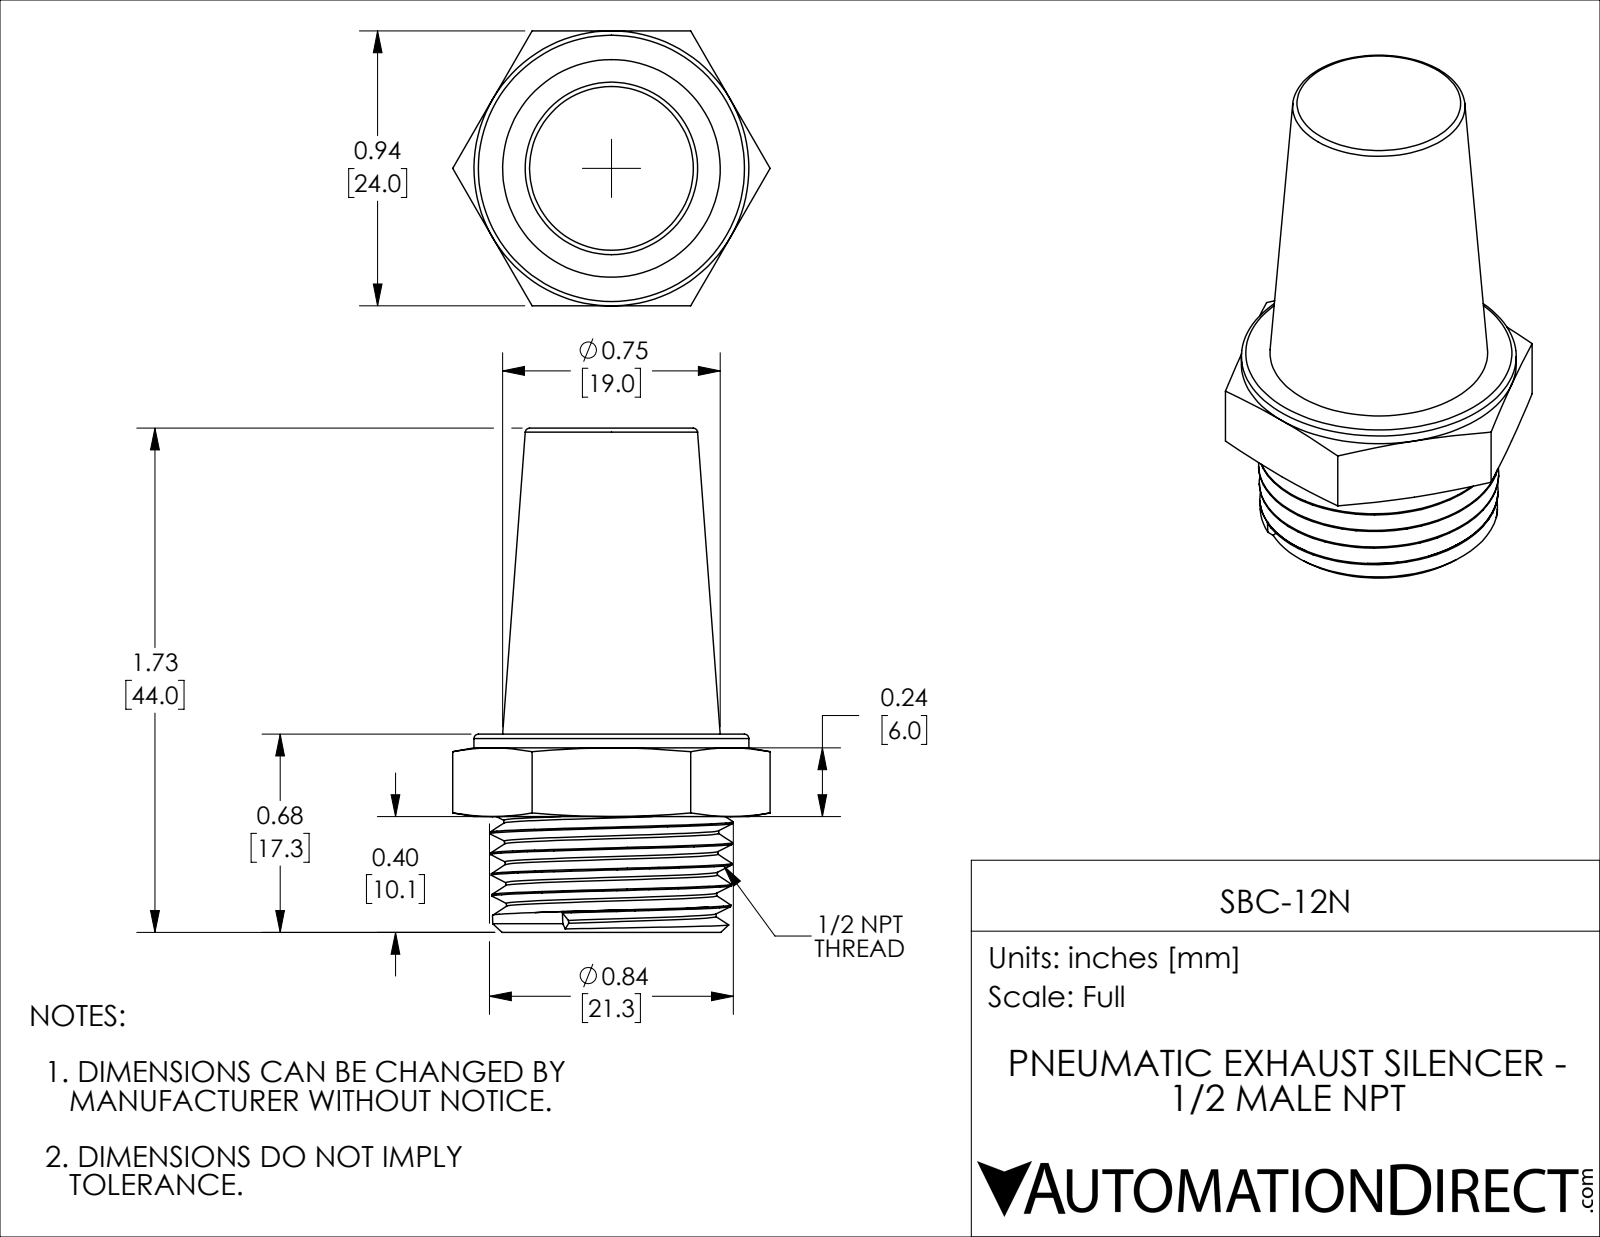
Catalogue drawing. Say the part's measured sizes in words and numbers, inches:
The part is named "SBC-12N". Its 3-D file was written by "SolidWorks 2021 (CONFIG_CONTROL_DESIGN)". It is 1 solid with 60 faces: 12 planar, 4 cylindrical and 44 other. Overall it measures 1.732 by 1.091 by 0.945 inches. Its volume is 0.736 cubic inches and its surface area 6.6 square inches. Round holes: 1 of diameter 0.314. Round bosses or shafts: 1 of diameter 0.945. The main face-to-face distances are 0.945, 1.732, 0.681, 1.051, 0.398, 0.283, 1.335, 0.5, 0.102, 0.181.
